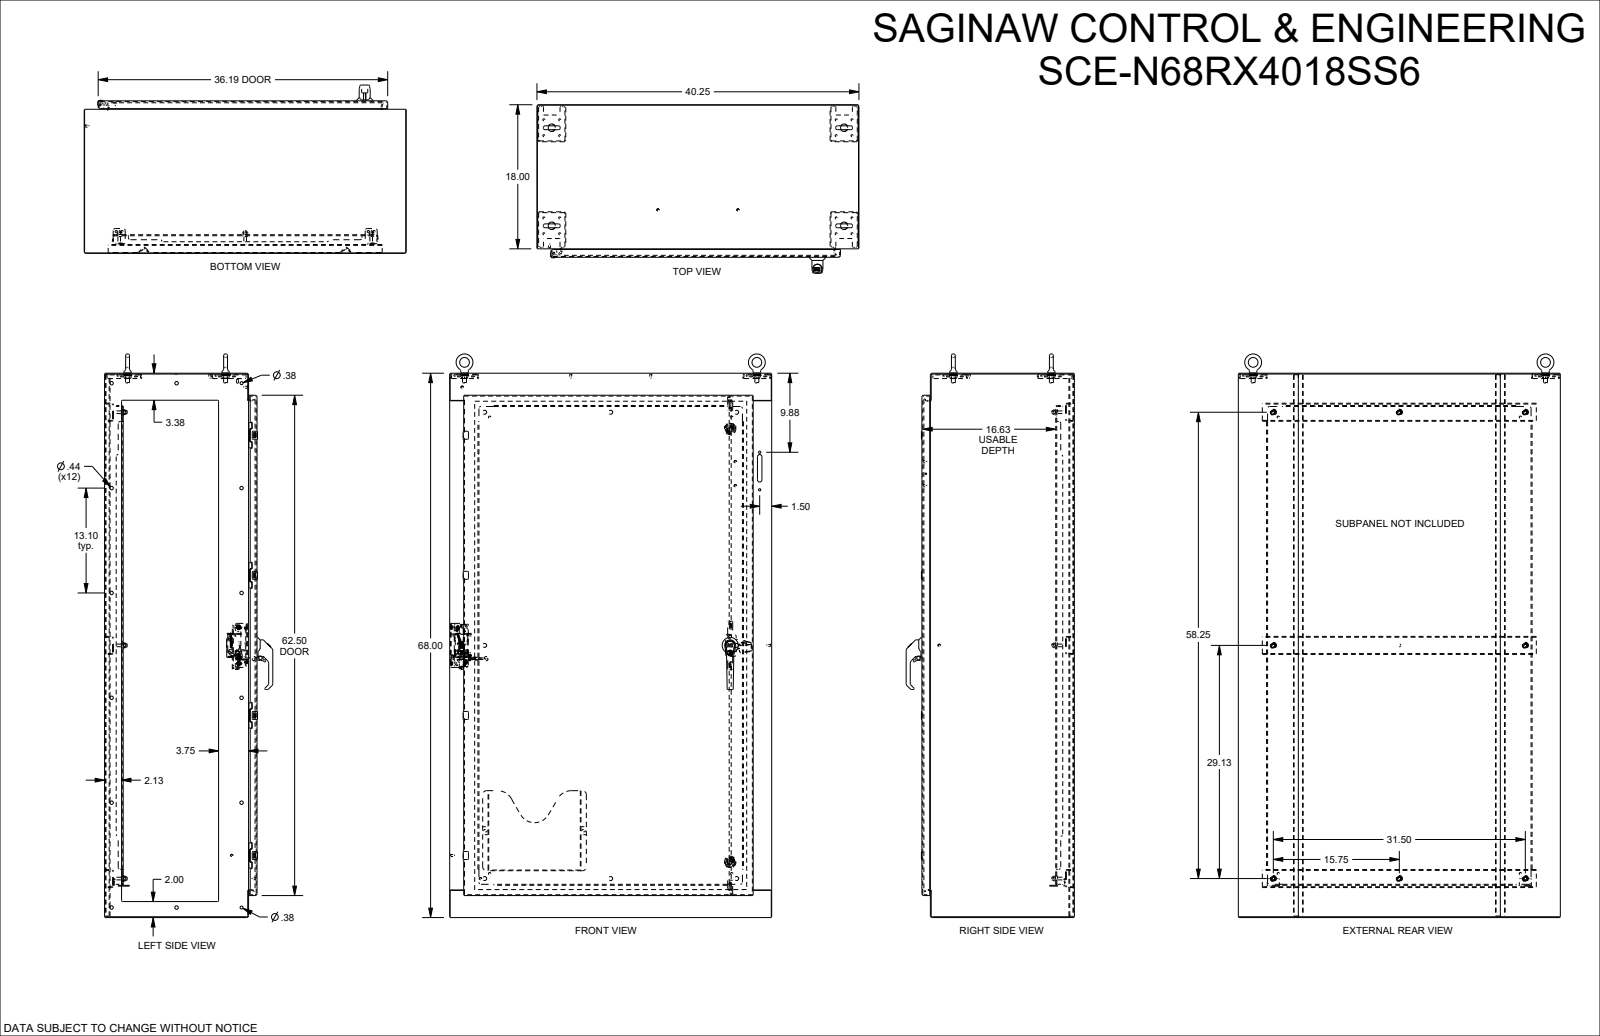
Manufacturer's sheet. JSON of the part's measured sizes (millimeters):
{"part_name": "SCE-N68RX4018", "step_written_by": "SolidWorks 2023 (AUTOMOTIVE_DESIGN)", "units": "millimeters", "bodies": {"solids": 31, "faces": 4314, "planar": 1670, "cylindrical": 1528, "other": 1116}, "overall_size": [1802, 1022.4, 534.6], "volume_mm3": 17370000, "surface_area_mm2": 12910000, "round_holes": [[6.4, 18], [11.1, 12], [9.5, 10], [5.2, 8], [6.2, 8], [1, 4], [4.3, 4], [5.5, 4], [6.5, 4], [22.2, 4], [2.9, 3], [5.1, 3]], "round_bosses_or_shafts": [[4.3, 12], [6.4, 10], [6.1, 8], [5, 5], [29.8, 4], [15.2, 4], [35.6, 2], [12.2, 2]], "partial_cylinders_radius": [[0.8, 142], [0.4, 108], [3.2, 83], [1.6, 52], [4.2, 38], [1, 37], [5.8, 32], [6.4, 26]], "face_to_face_distances": [2.6, 481.4, 478.8, 484.1, 2.6, 1724.6, 454.6, 26.9, 1019.7, 1721.9], "hole_center_spacings": [50.3, 35.6, 444.5, 332.7, 530.2, 71.1, 287.1, 311.2]}
